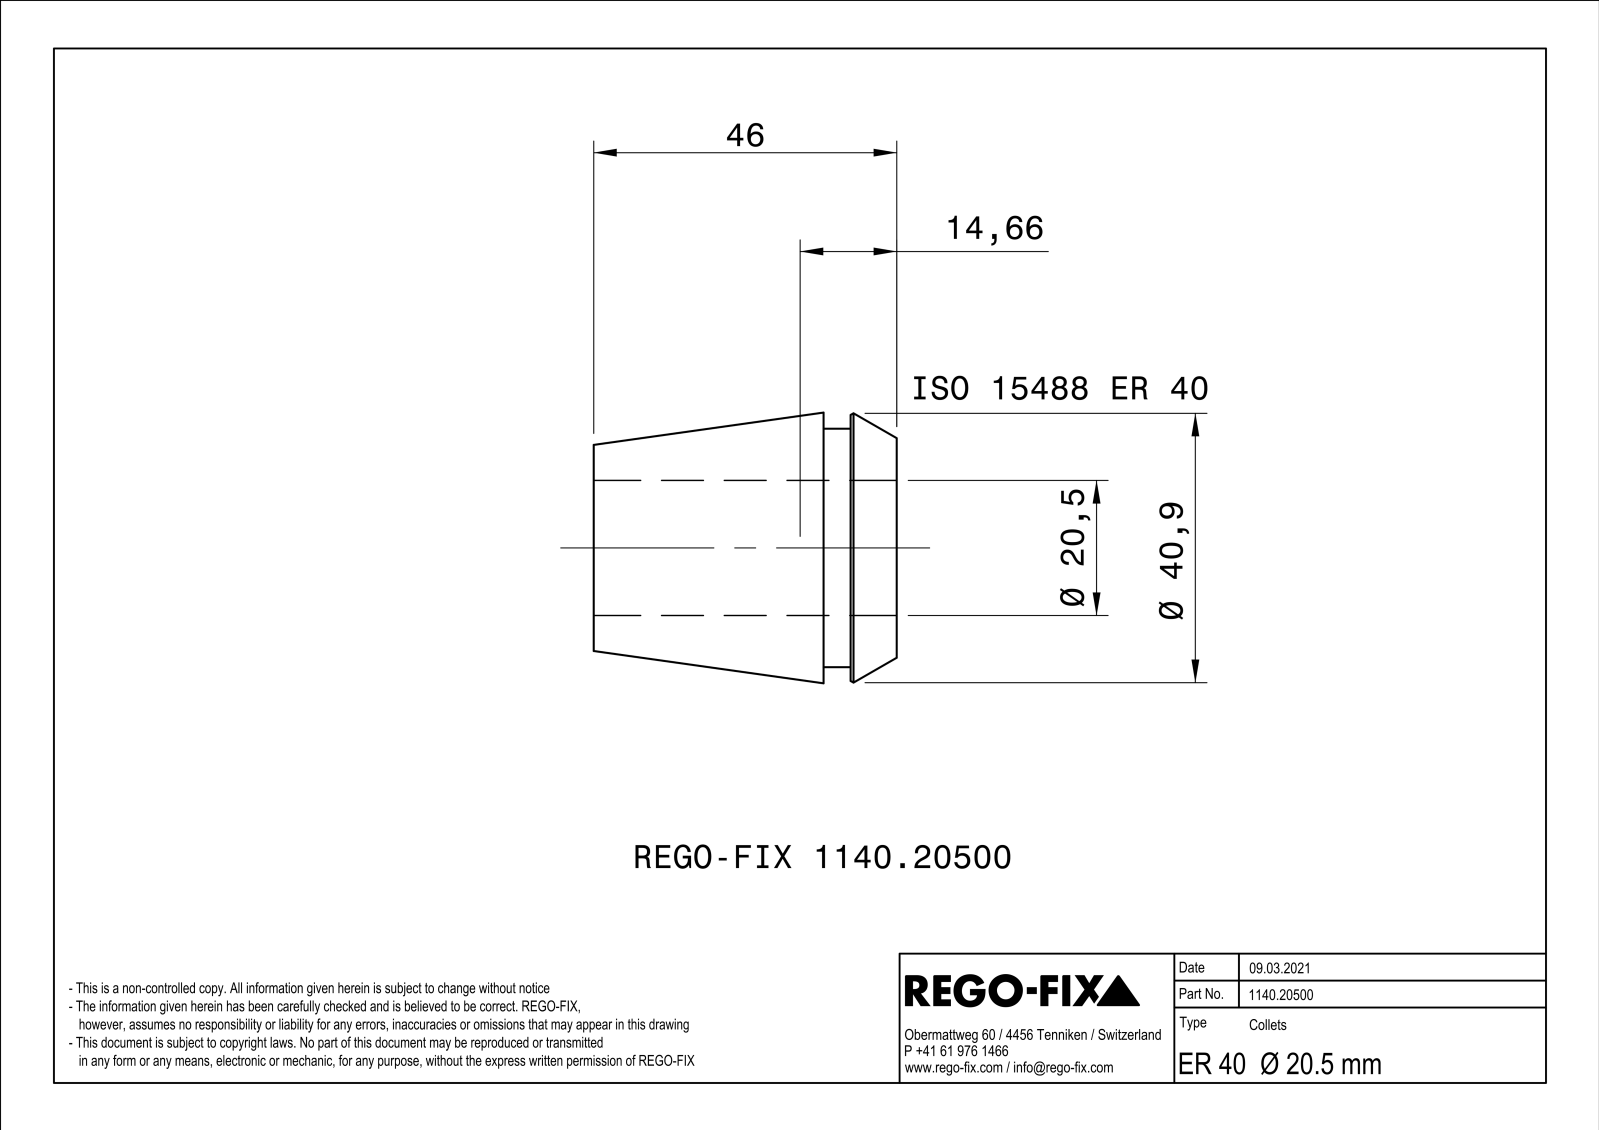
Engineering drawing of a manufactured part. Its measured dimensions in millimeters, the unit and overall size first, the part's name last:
Units: millimetres
Overall size (bounding box): 46 × 40.99 × 40.99
Round holes (diameter × count): ⌀20.5 ×1
Round bosses / shafts (diameter × count): ⌀36.2 ×1
Main face-to-face distances: 1, 46, 11.1, 34.9, 7, 4.1, 39, 7.5, 0.5, 3.6
Volume: 27 498 mm³ · Surface area: 18 799 mm²
Bodies: 1 solid, 177 faces (88 planar, 9 cylindrical, 80 other)
Part name (STEP PRODUCT): NOCUT
STEP written by: SIEMENS PLM Software Solid Edge ST10 (AUTOMOTIVE_DESIGN)
